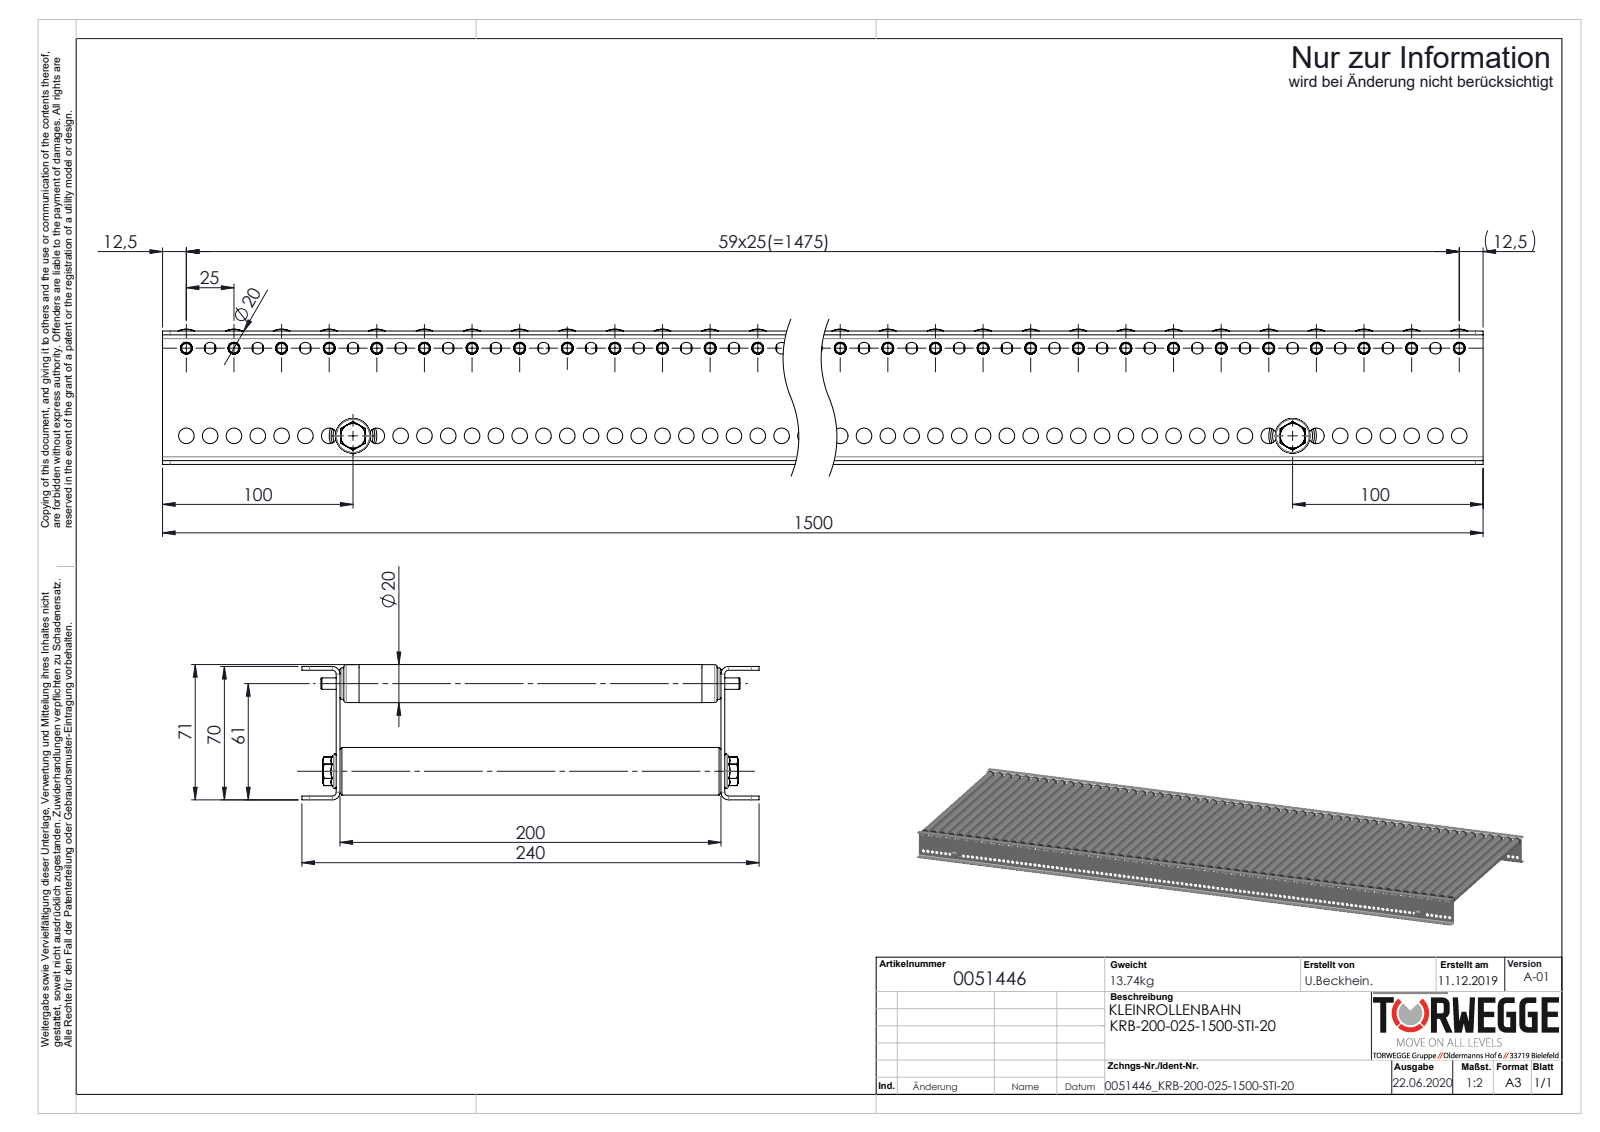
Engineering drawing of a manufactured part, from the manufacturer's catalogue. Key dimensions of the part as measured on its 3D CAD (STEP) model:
Part name (STEP PRODUCT): Profil_KRB-20x70x20x2_KFG_S100205_U-PROFIL-20-70-20-2-KRB-20-L=1500; 0039777_Achse-Ø06-FA-KFG_L=220 fr D20; 0051446; Traversen_KFG_L200 (+4 more)
STEP written by: SolidWorks 2020 (AUTOMOTIVE_DESIGN)
Units: millimetres
Bodies: 132 solids, 11792 faces (3840 planar, 4488 cylindrical, 3464 other)
Overall size (bounding box): 1500 × 240 × 71
Volume: 1 685 000 mm³ · Surface area: 2 617 000 mm²
Round holes (diameter × count): ⌀6.2 ×119, ⌀8.2 ×119, ⌀6.1 ×60, ⌀14.2 ×60, ⌀17.2 ×60, ⌀18 ×60, ⌀6.8 ×2, ⌀21 ×2
Round bosses / shafts (diameter × count): ⌀20 ×60, ⌀19.9 ×60, ⌀18.1 ×60, ⌀17.8 ×60, ⌀16.5 ×60, ⌀6 ×60, ⌀25 ×2, ⌀8 ×2
Partial cylindrical surfaces — rounded edges, fillets, slot ends (radius × count): R4.05 ×60, R4 ×8, R2 ×4
Main face-to-face distances: 2, 202, 68, 200, 204, 70, 66, 192, 18, 30
Hole centre spacings: 12.5, 25, 37.5, 50, 62.5, 75, 87.5, 100
